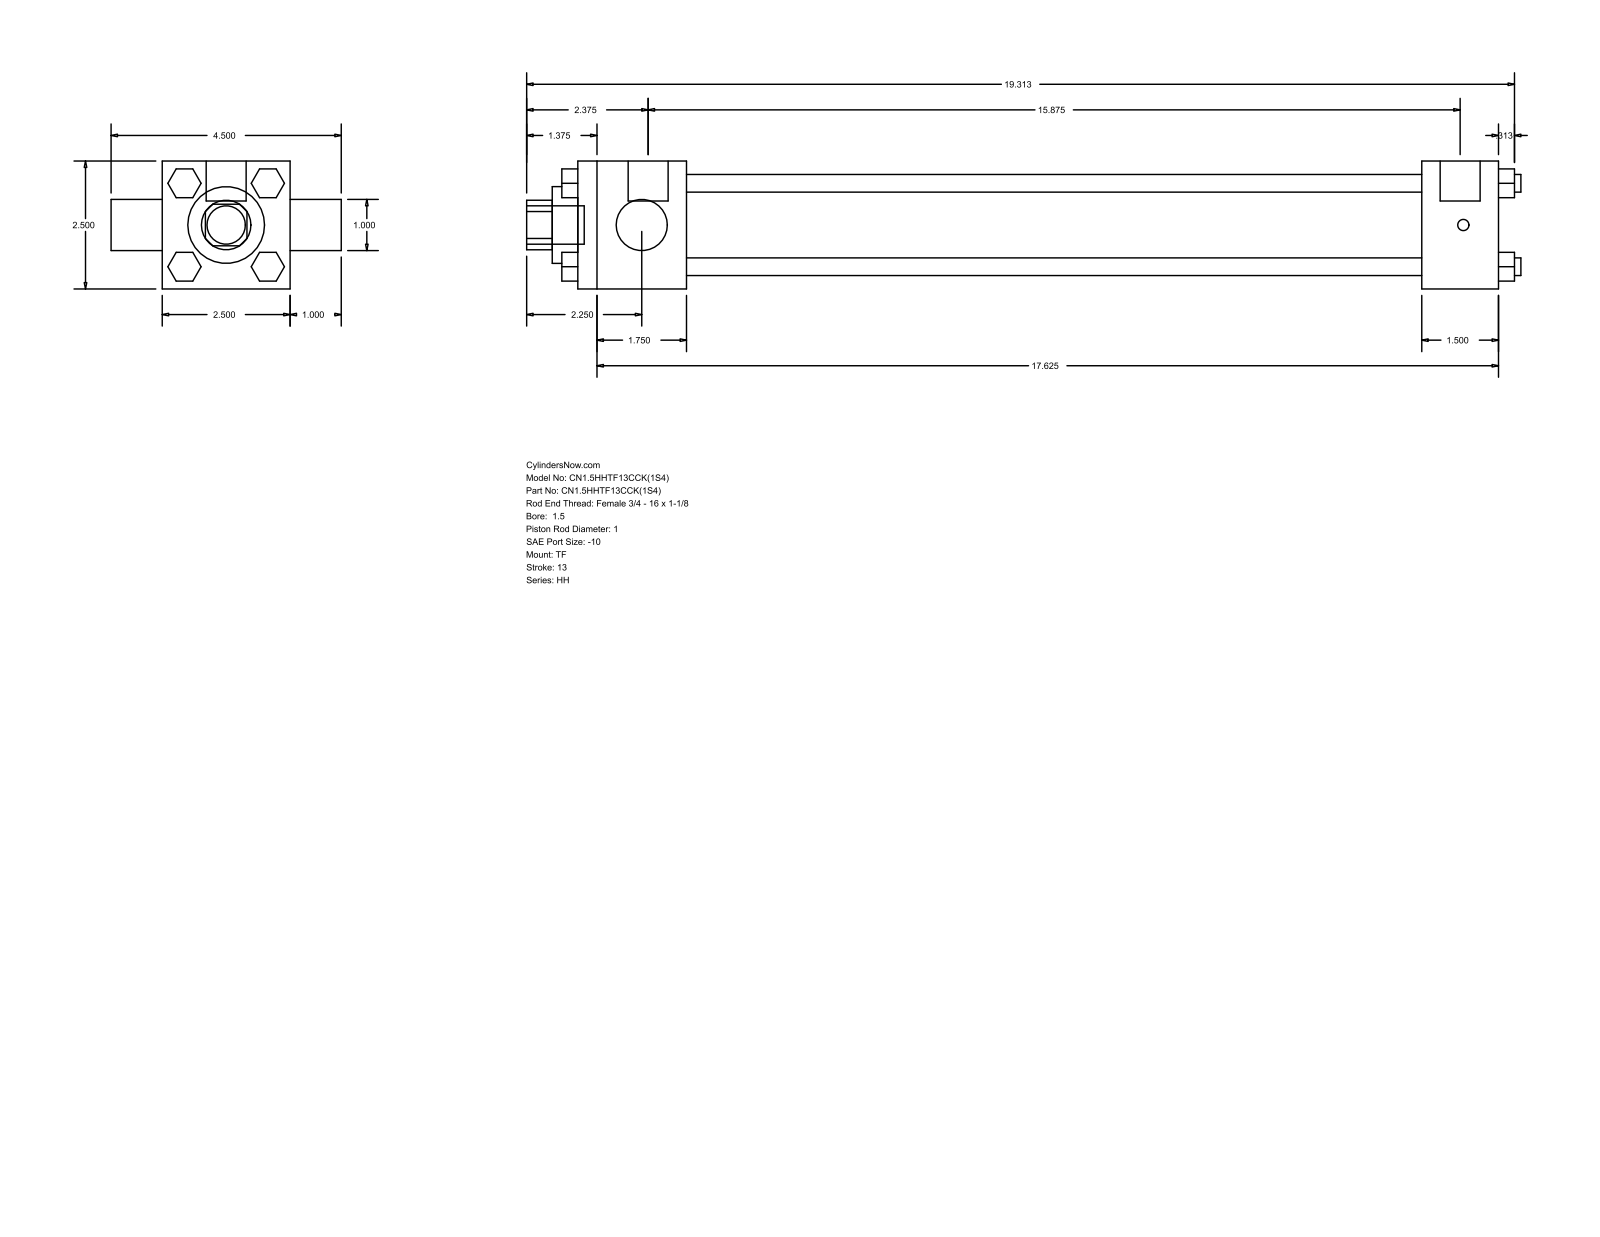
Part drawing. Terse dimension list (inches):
name: HH_TF__0150_1
written by: GSSL Pune (CONFIG_CONTROL_DESIGN)
unit: in
bodies: 0 solids, 120 faces (92 planar, 28 cylindrical, 0 other)
size: 19.437 × 4.5 × 2.5
holes: 2× ⌀1, 1× ⌀1.5, 1× ⌀1.75
bosses: 4× ⌀0.345, 3× ⌀0.219, 2× ⌀0.781, 1× ⌀0.75
rounds: 1× R0.484
face distances: 2.5, 15.875, 14.375, 1.5, 2.125, 16.5, 18, 18.313, 1, 0.815
